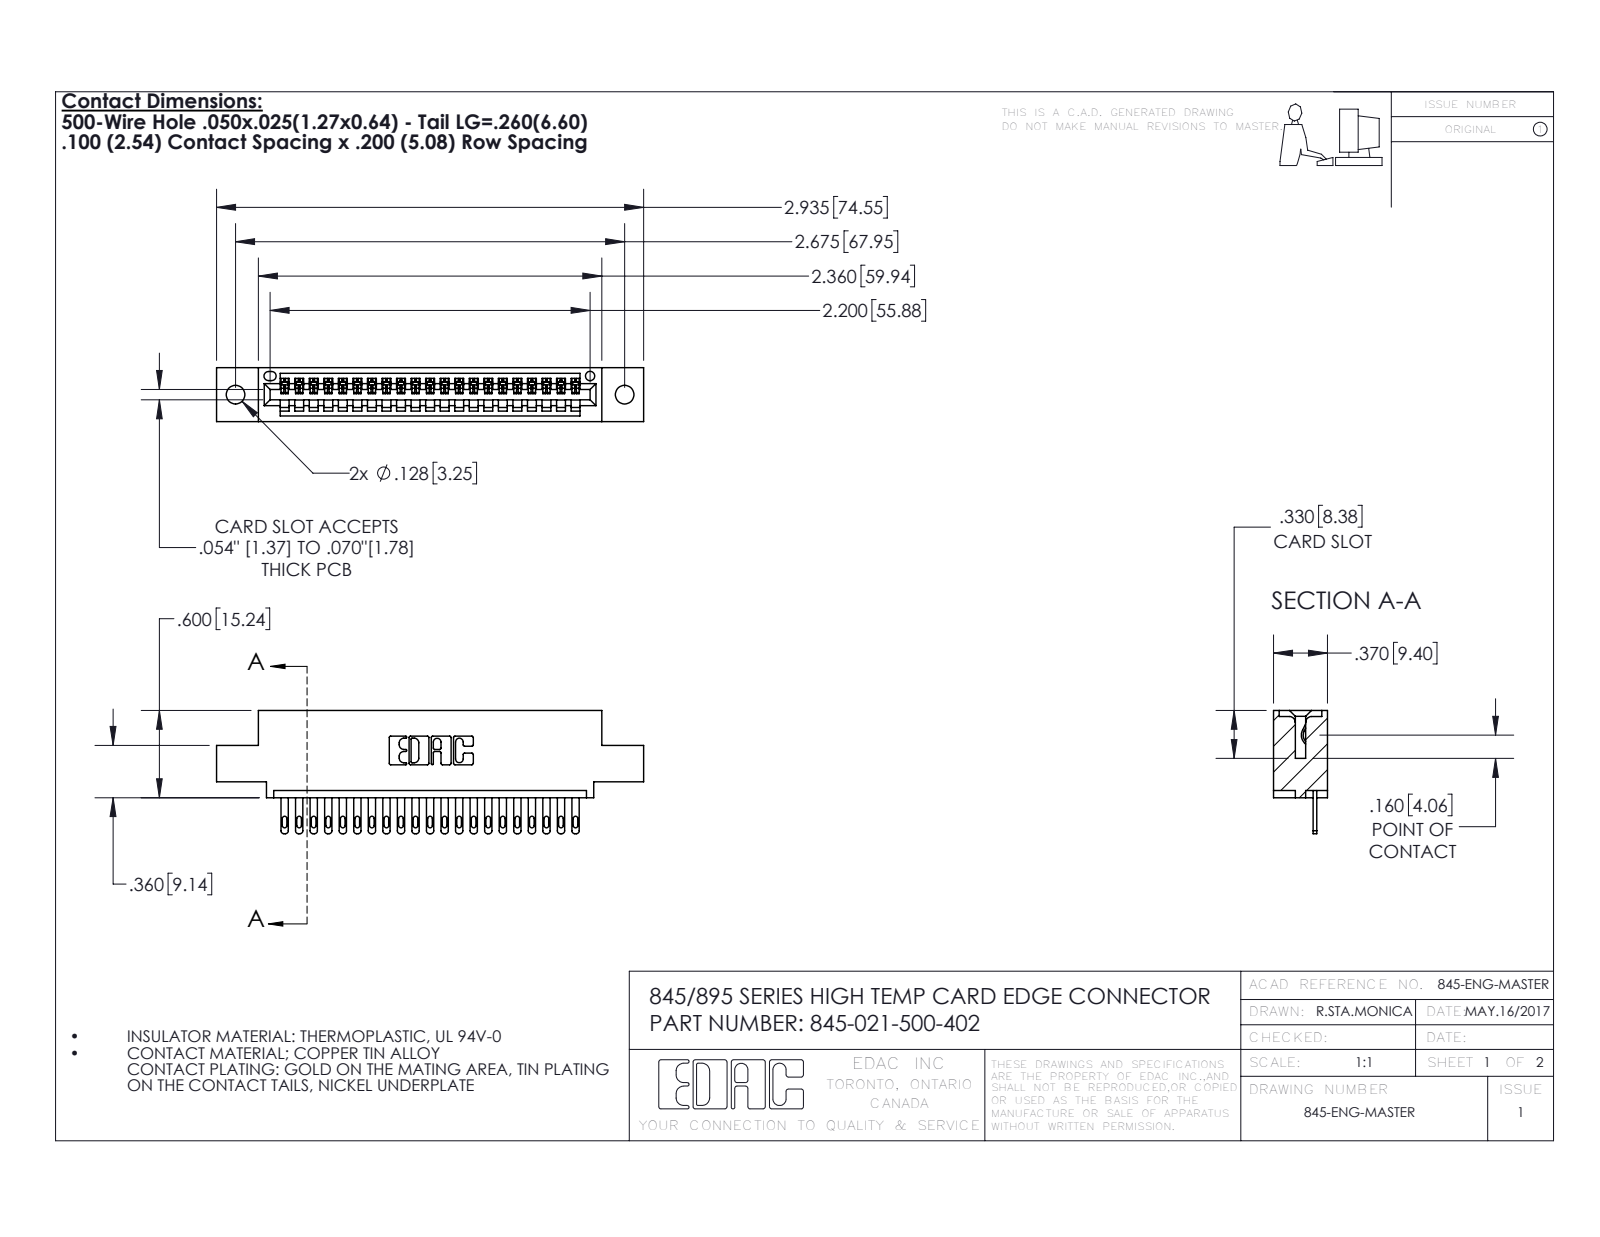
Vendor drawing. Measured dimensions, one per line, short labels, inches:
name: 345-292-001_345-293-100; 345-021-500-402; 345 Part_0.110 Offset - 0.128 Dia
written by: SolidWorks 2016 (CONFIG_CONTROL_DESIGN)
unit: in
bodies: 22 solids, 1264 faces (798 planar, 466 cylindrical, 0 other)
size: 2.935 × 0.847 × 0.37
volume: 0.416 in³; area: 13.37 in²
holes: 2× ⌀0.128, 1× ⌀0.064
rounds: 42× R0.006, 42× R0.016, 42× R0.02, 22× R0.01, 6× R0.007, 6× R0.031, 3× R0.026, 2× R0.031
face distances: 0.298, 0.072, 0.2, 0.37, 0.098, 0.272, 0.025, 0.225, 0.149, 0.072
hole spacings: 0.27, 2.441, 2.675
